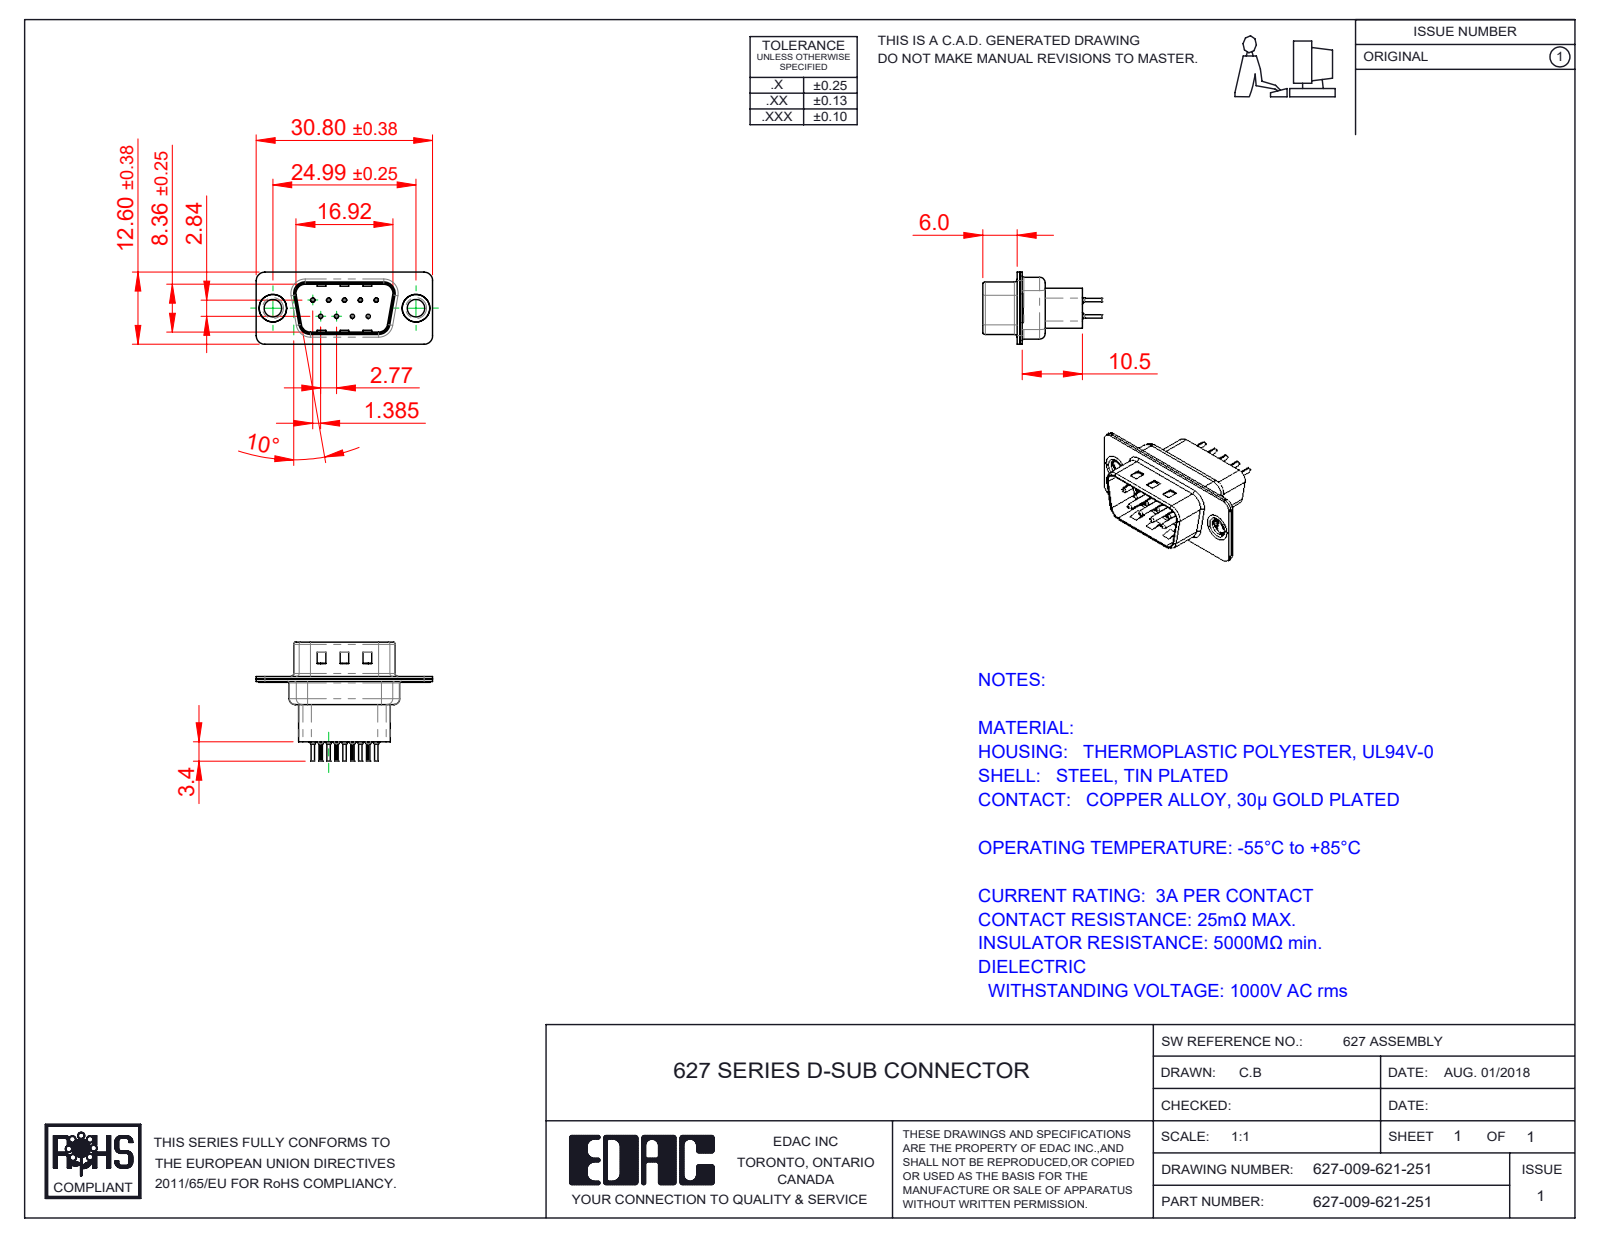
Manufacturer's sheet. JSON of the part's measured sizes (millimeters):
{"part_name": "627 Shell Rear_09 Contacts; 627 Shell Front_09 Contacts; 627 Thru Hole Rivet; 627 Housing_09 HP (+3 more)", "step_written_by": "SolidWorks 2020 (CONFIG_CONTROL_DESIGN)", "units": "millimeters", "bodies": {"solids": 14, "faces": 1160, "planar": 323, "cylindrical": 446, "other": 391}, "overall_size": [30.8, 20.8, 12.6], "volume_mm3": 1694, "surface_area_mm2": 4554, "round_holes": [[0.2, 9], [0.35, 9], [1.1, 9], [1.6, 9], [3.05, 2], [4, 2], [4.8, 2]], "round_bosses_or_shafts": [[2, 9], [1.5, 9], [0.75, 9], [0.6, 9], [5, 2], [4.9, 2], [3.55, 2]], "partial_cylinders_radius": [[0.1, 18], [1.5, 18], [2, 12], [0.5, 8], [1.6, 8], [0.25, 4], [0.6, 4], [0.65, 4]], "face_to_face_distances": [0.45, 0.4, 0.9, 0.82, 9.58, 1.4, 1.5, 0.68, 7.68, 1.08], "hole_center_spacings": [3.16, 2.77, 5.54, 5.03, 5.04, 8.31, 7.48, 7.49]}
